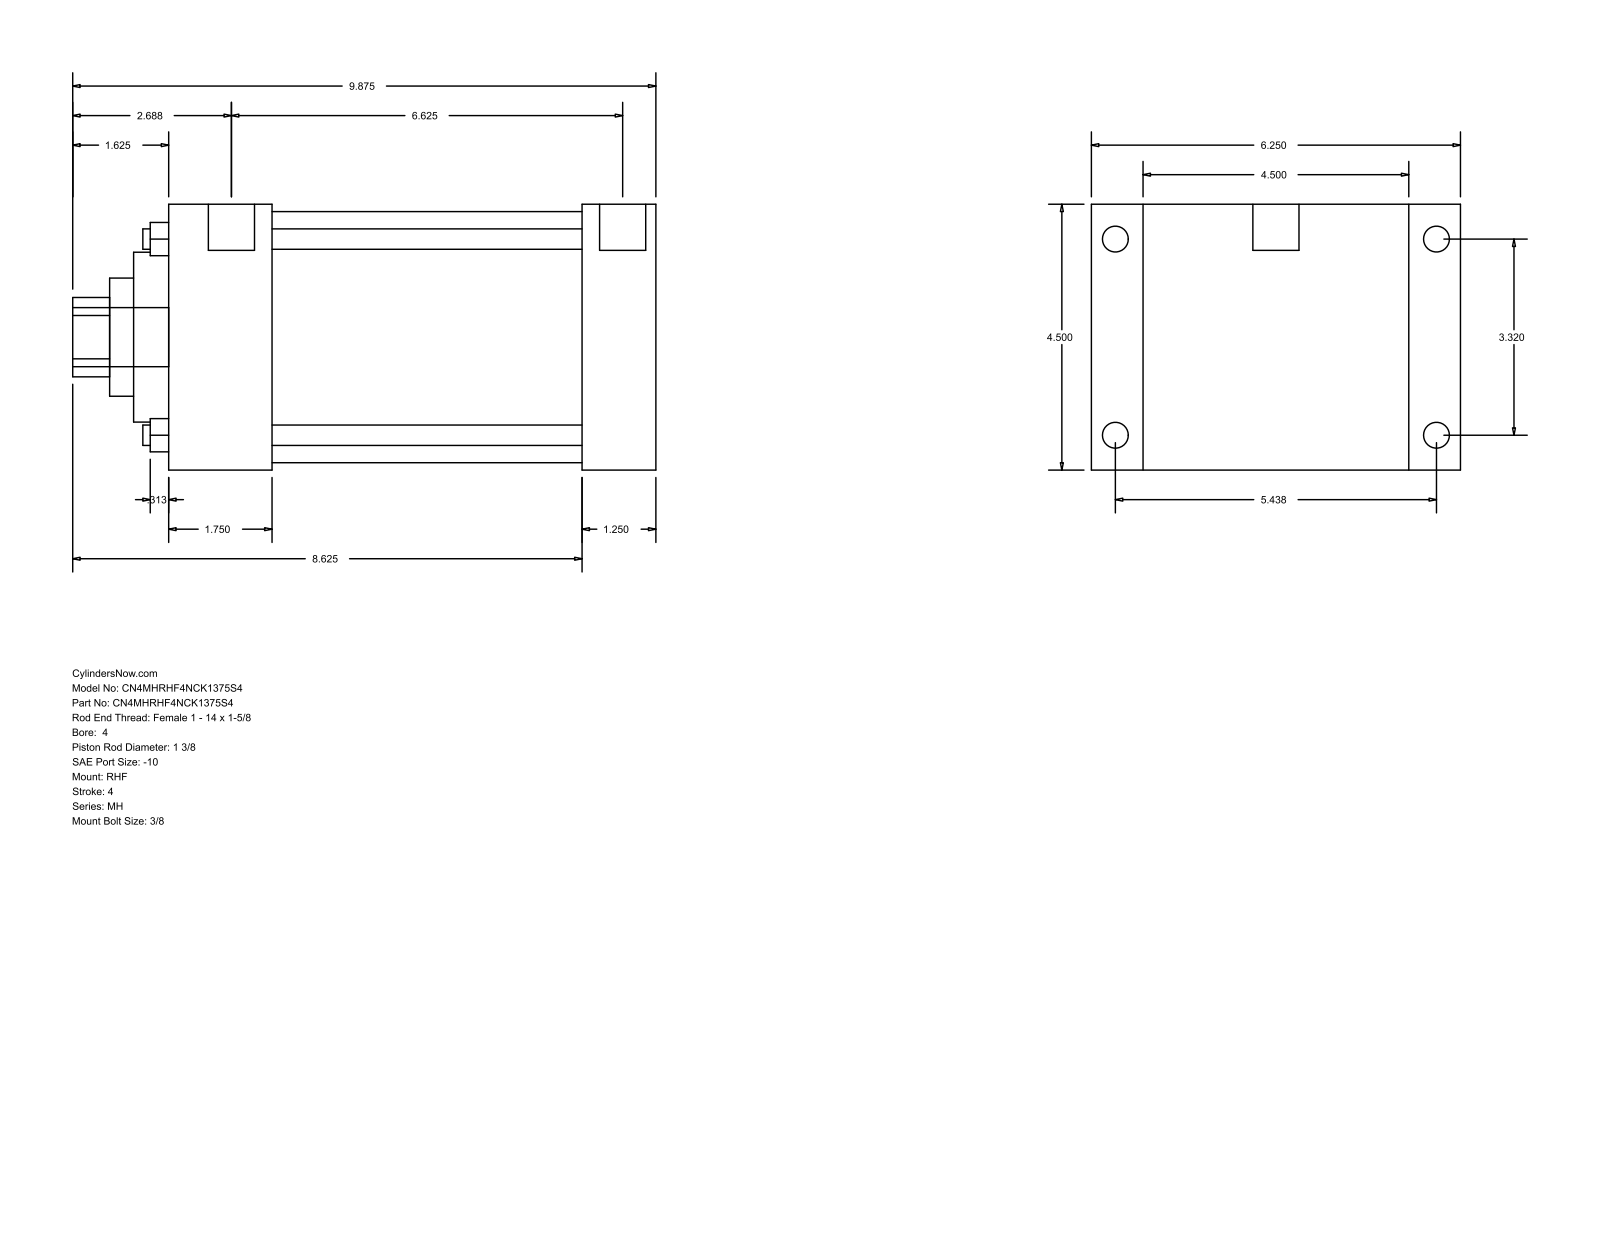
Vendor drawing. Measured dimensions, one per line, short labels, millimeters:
name: MH_RHF__0400_1.375
written by: GSSL Pune (CONFIG_CONTROL_DESIGN)
unit: mm
bodies: 0 solids, 90 faces (61 planar, 29 cylindrical, 0 other)
size: 250.82 × 158.75 × 114.3
holes: 4× ⌀8.76, 1× ⌀34.92, 1× ⌀50.8, 1× ⌀73.03, 1× ⌀107.95
bosses: 4× ⌀11.13, 4× ⌀8.73, 2× ⌀19.84, 1× ⌀25.4
rounds: 1× R17.06
face distances: 114.3, 209.55, 177.8, 31.75, 22.23, 136.53, 44.45, 133.35, 165.1, 158.76
hole spacings: 59.62, 84.32, 119.25
